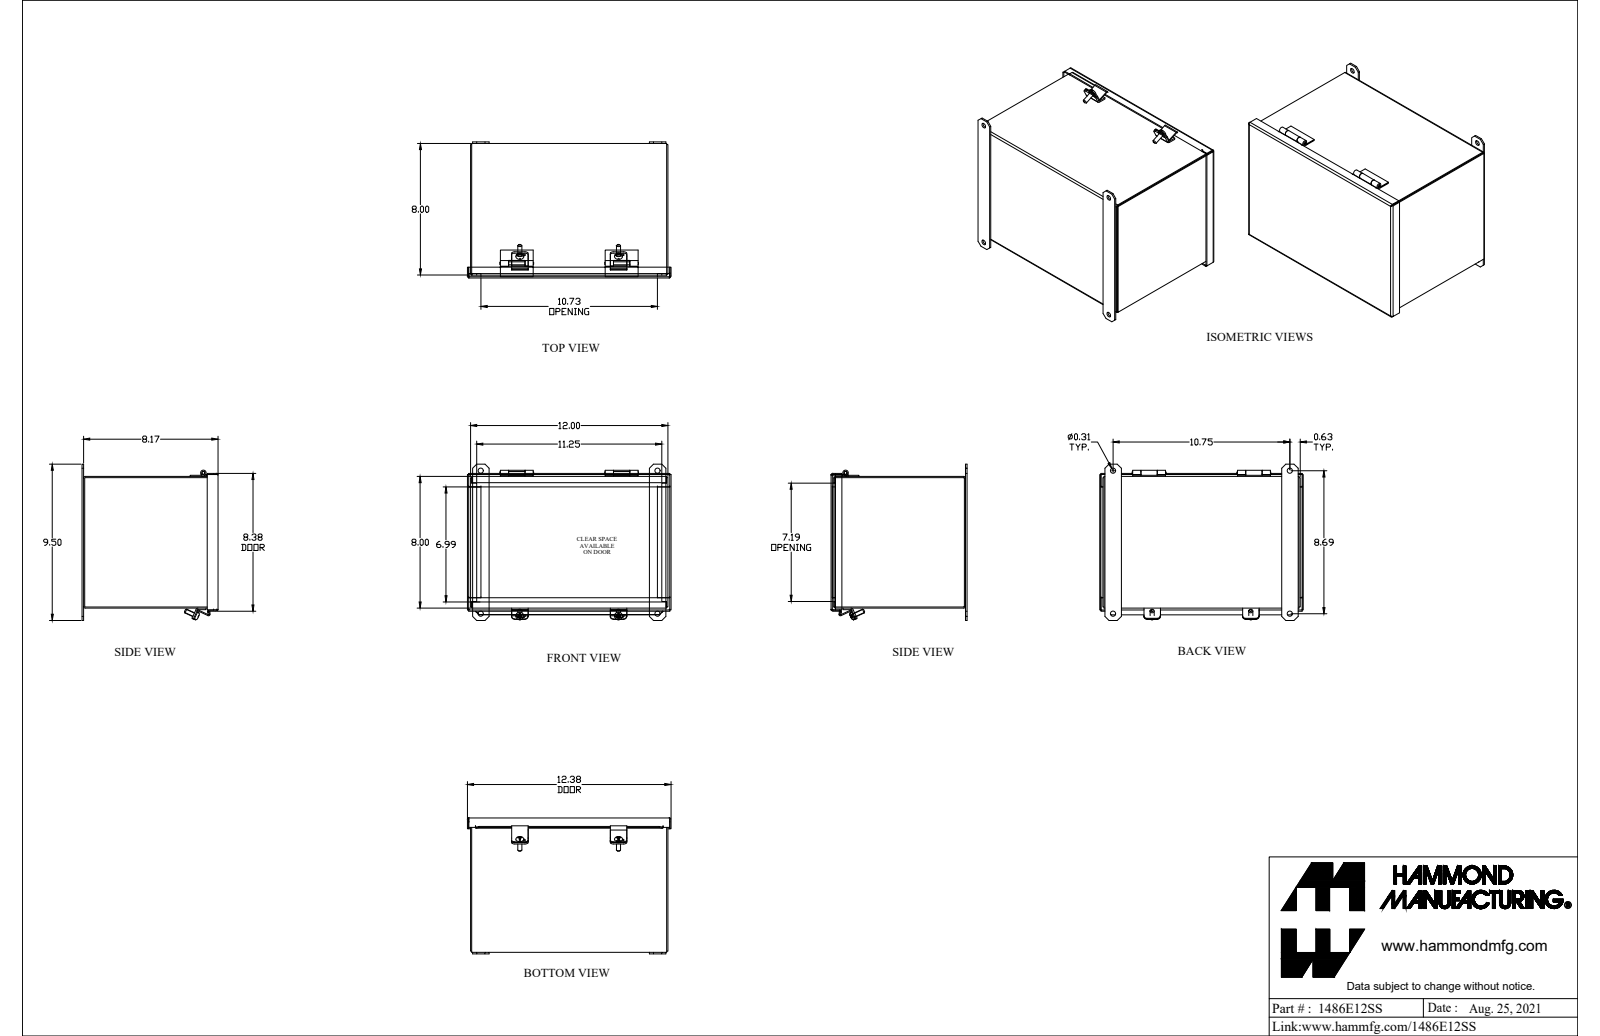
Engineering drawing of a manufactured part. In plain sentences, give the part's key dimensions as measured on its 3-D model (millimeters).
The part is named "1486E12". Its 3-D file was written by "SolidWorks 2021 (AUTOMOTIVE_DESIGN)". It is 9 solids with 382 faces: 270 planar, 92 cylindrical and 20 other. Overall it measures 314.3 by 241.3 by 210 millimeters. Its volume is 779 200 cubic millimeters and its surface area 778 700 square millimeters. Round holes: 4 of diameter 8, 2 of diameter 5.4, 1 of diameter 4.7. Round bosses or shafts: 2 of diameter 12.3, 2 of diameter 6.4, 1 of diameter 8.6, 1 of diameter 4.6. Partial cylindrical surfaces (rounded edges, fillets, slot ends): 11 of radius 0.9, 11 of radius 2.7, 8 of radius 4.8, 4 of radius 0.3, 4 of radius 0.8, 4 of radius 3.6, 2 of radius 0.7, 2 of radius 2.2. The main face-to-face distances are 1.8, 201.4, 205.7, 303, 199.5, 203.2, 203.9, 207.6, 4.7, 301.1. The hole center spacings are 220.7, 152.4, 273.1, 273.1, 351.1, 351.1.
